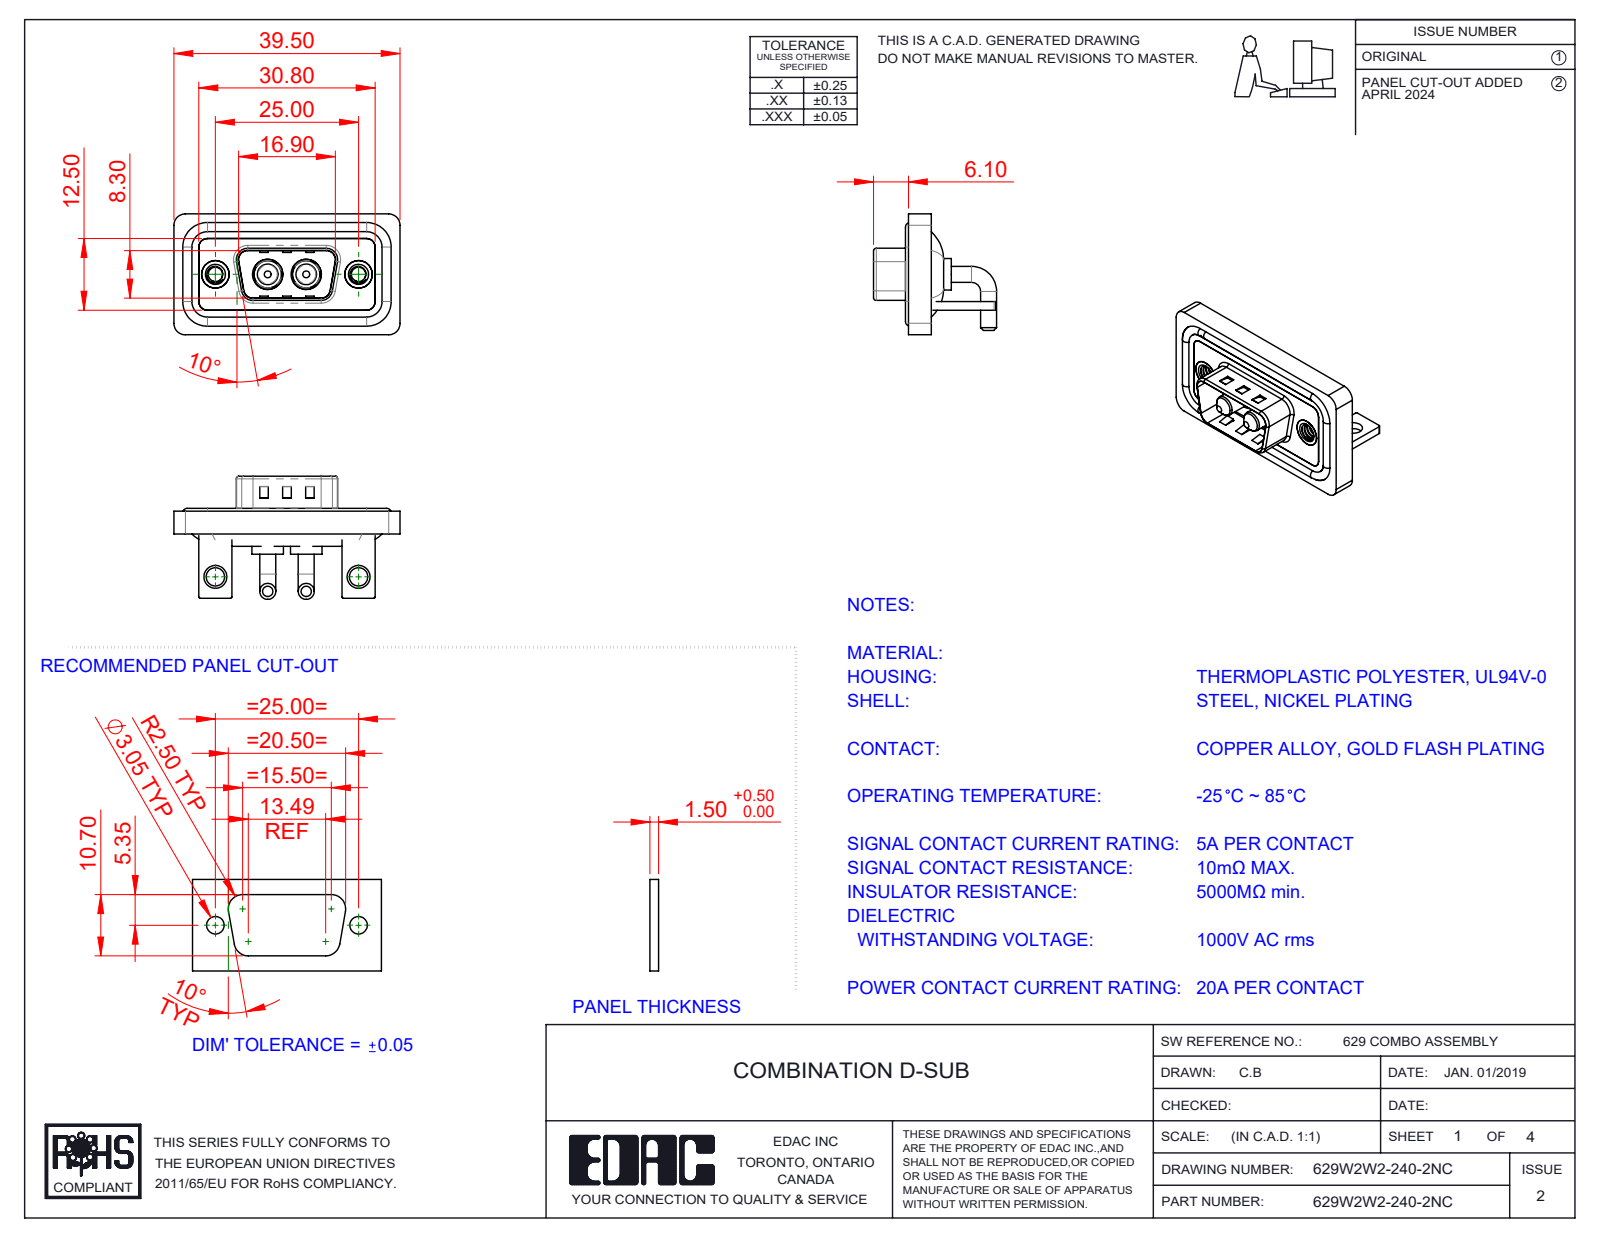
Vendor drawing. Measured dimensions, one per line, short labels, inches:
name: Power Pin_20A RA; 629W2W2-140-2NC; 629Combo Stabilizer Bracket; 629Combo Housing_2W2 (+4 more)
written by: SolidWorks 2023 (CONFIG_CONTROL_DESIGN)
unit: in
bodies: 13 solids, 535 faces (185 planar, 240 cylindrical, 110 other)
size: 1.555 × 0.846 × 0.831
volume: 0.296 in³; area: 12.02 in²
holes: 2× ⌀0.098, 2× ⌀0.126, 2× ⌀0.157, 2× ⌀0.189, 2× ⌀0.191, 2× ⌀0.197, 2× ⌀0.209
bosses: 4× ⌀0.11, 4× ⌀0.063, 2× ⌀0.217, 2× ⌀0.205, 2× ⌀0.193, 2× ⌀0.187, 2× ⌀0.148, 2× ⌀0.142
rounds: 19× R0.079, 18× R0.059, 16× R0.01, 9× R0.02, 8× R0.063, 4× R0.024, 4× R0.026, 4× R0.035
face distances: 0.016, 0.059, 0.114, 0.031, 0.043, 0.047, 0.083, 0.063, 0.146, 0.098
hole spacings: 0.36, 0.624, 0.984, 0.265
